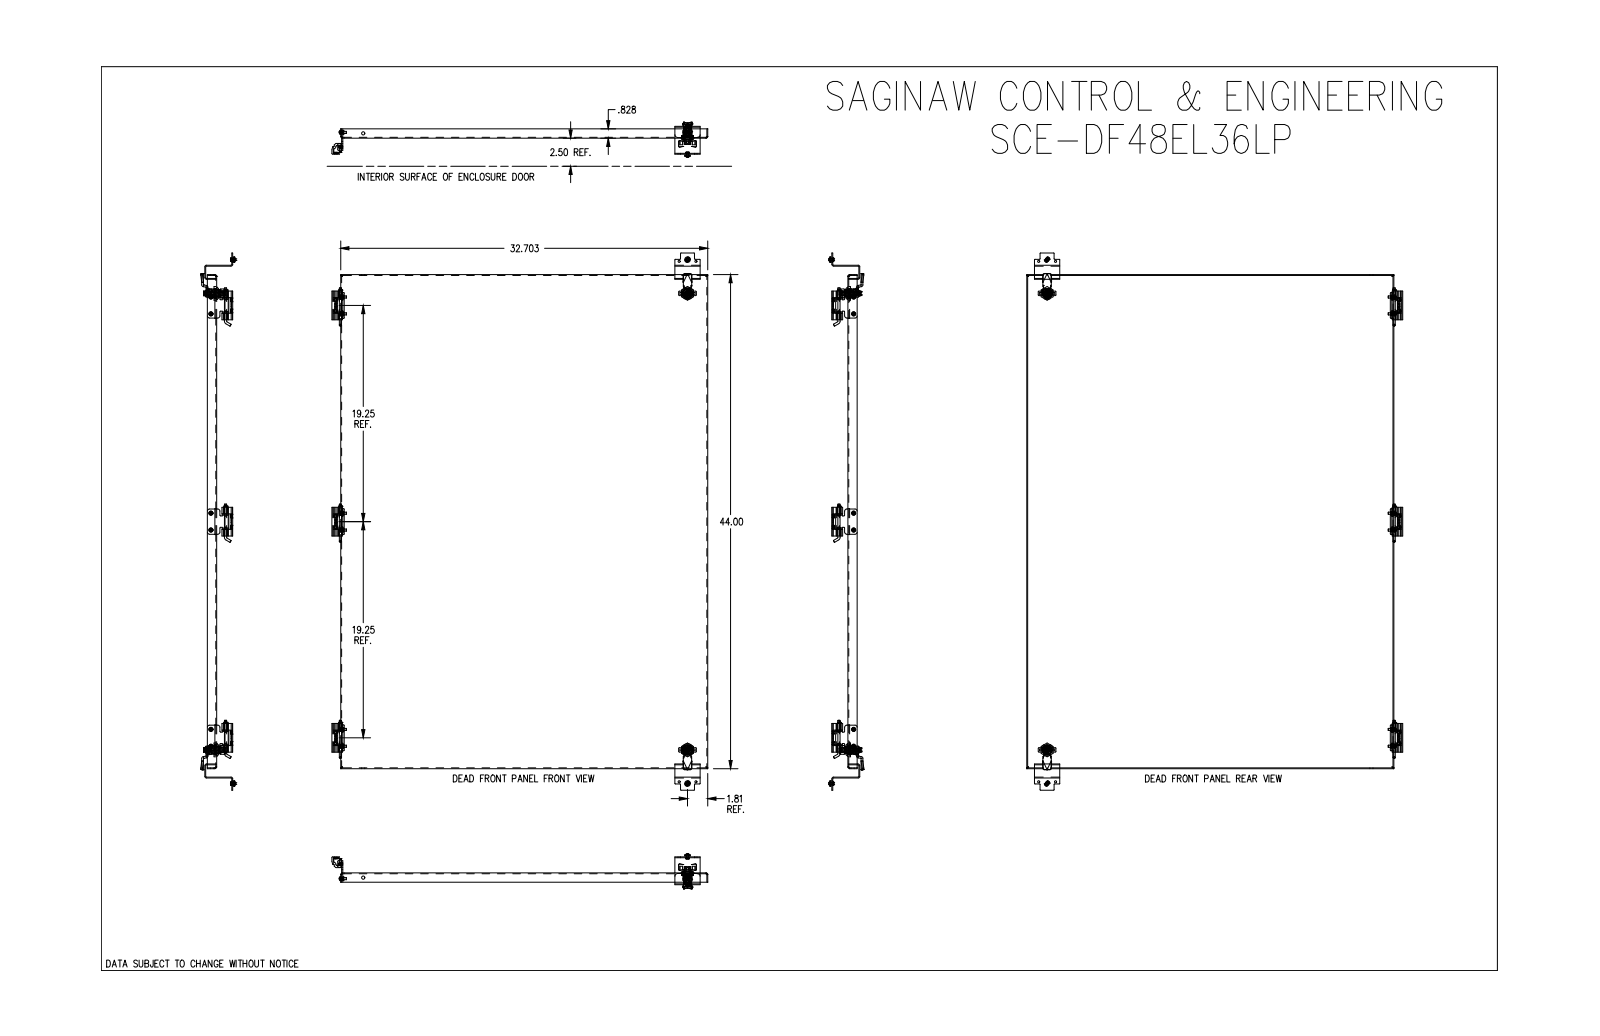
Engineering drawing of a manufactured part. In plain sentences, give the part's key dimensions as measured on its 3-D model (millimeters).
The part is named "SCE-DF48EL36LP". Its 3-D file was written by "SolidWorks 2021 (AUTOMOTIVE_DESIGN)". It is 46 solids with 1469 faces: 764 planar, 382 cylindrical and 323 other. Overall it measures 1215.1 by 850.7 by 79.2 millimeters. Its volume is 1 660 000 cubic millimeters and its surface area 2 121 000 square millimeters. Round holes: 8 of diameter 4.8, 8 of diameter 6.4, 6 of diameter 4.3, 6 of diameter 5.3, 4 of diameter 4.8, 2 of diameter 5, 2 of diameter 6.3, 2 of diameter 10, 2 of diameter 11, 2 of diameter 16.1, 1 of diameter 5.6. Round bosses or shafts: 8 of diameter 8.6, 6 of diameter 9.5, 6 of diameter 6.3, 6 of diameter 4.8, 4 of diameter 5, 2 of diameter 28, 2 of diameter 19.8, 2 of diameter 16. Partial cylindrical surfaces (rounded edges, fillets, slot ends): 16 of radius 4, 13 of radius 1.3, 9 of radius 1.5, 9 of radius 1.7, 8 of radius 1.5, 8 of radius 2, 7 of radius 1.6, 7 of radius 2.6. The main face-to-face distances are 1.5, 1.5, 829.1, 1116.1, 830.7, 827.6, 2, 1117.6, 1114.6, 21. The hole center spacings are 489, 38.1, 19.5, 977.9, 1104.9, 1181.1, 25, 74.7.
